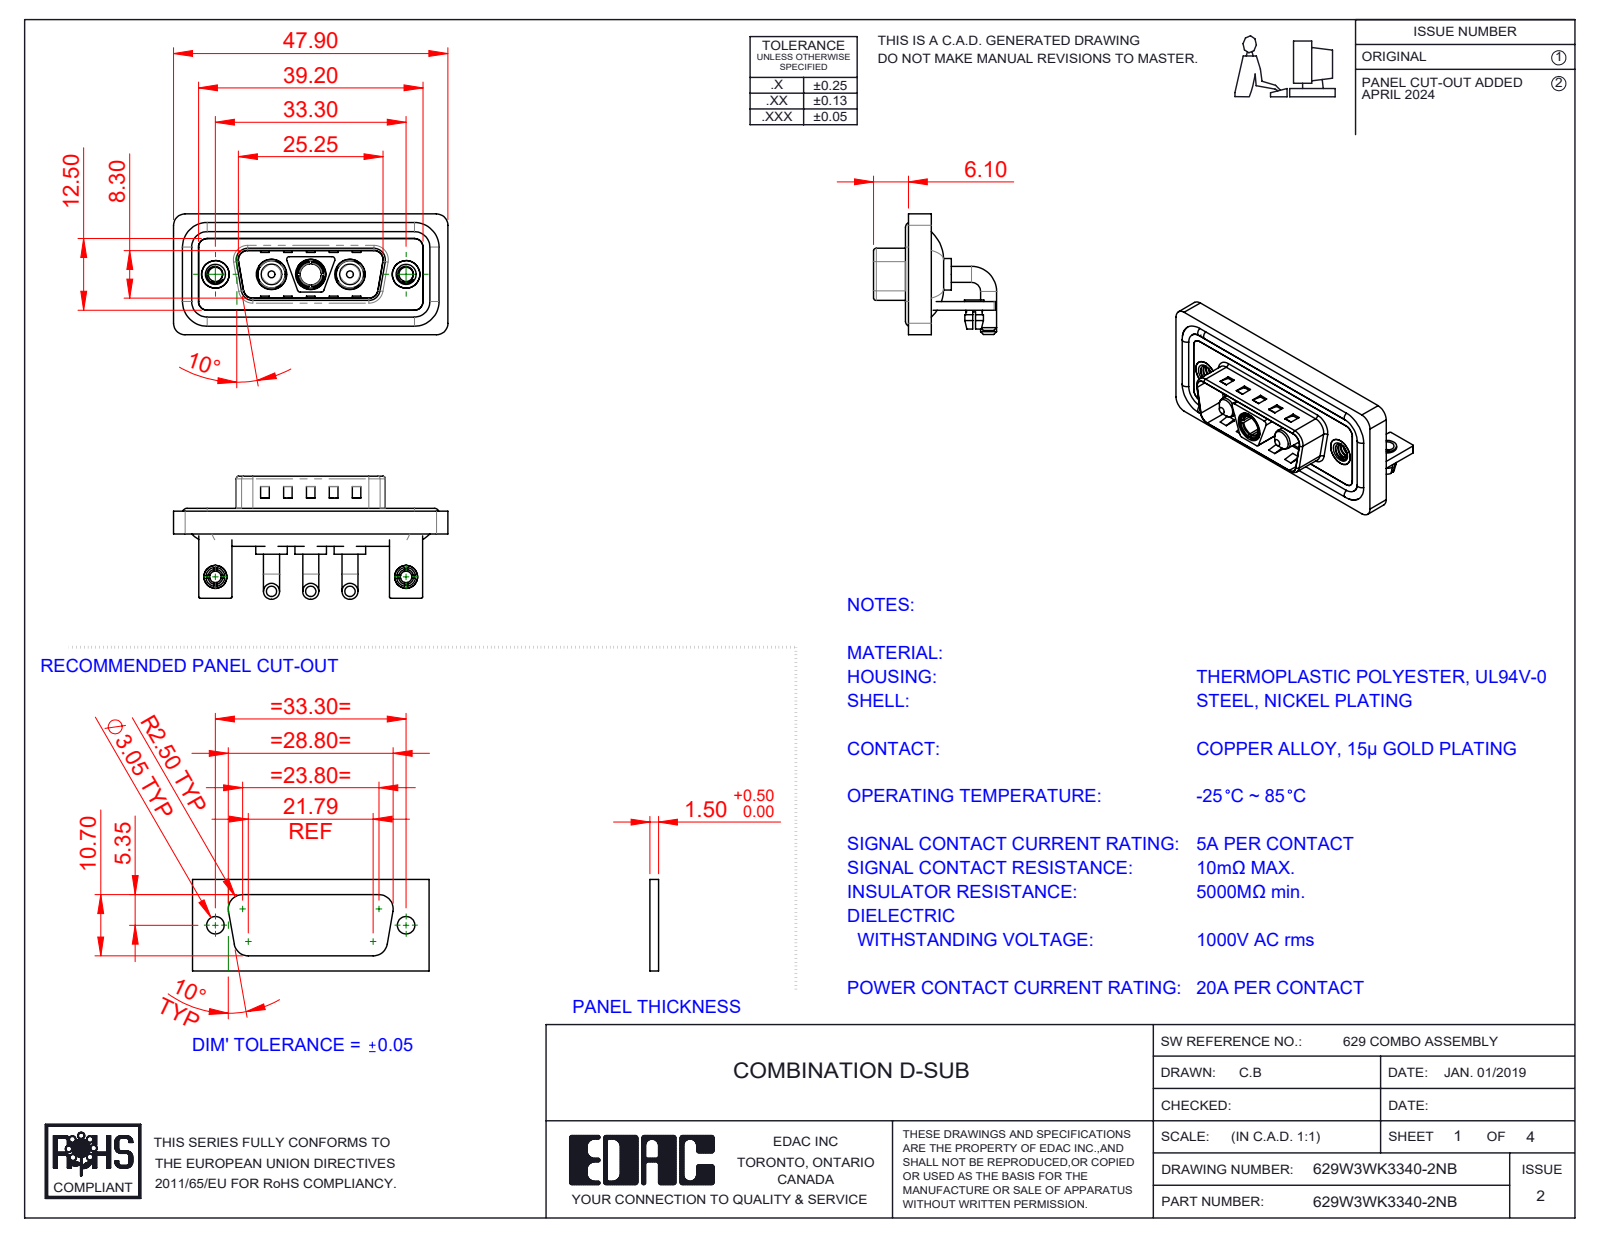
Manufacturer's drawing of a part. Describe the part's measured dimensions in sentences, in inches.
The part is named "629Combo Shell Rear_15 Contacts; 629Combo Stabilizer Bracket; 629Combo Waterproof Housing_15 Contacts; 629Combo Housing_3WK3 (+6 more)". Its 3-D file was written by "SolidWorks 2023 (CONFIG_CONTROL_DESIGN)". It is 17 solids with 751 faces: 299 planar, 306 cylindrical and 146 other. Overall it measures 1.886 by 0.846 by 0.831 inches. Its volume is 0.378 cubic inches and its surface area 15.83 square inches. Round holes: 4 of diameter 0.098, 3 of diameter 0.191, 3 of diameter 0.209, 2 of diameter 0.079, 2 of diameter 0.126, 2 of diameter 0.157, 2 of diameter 0.189, 2 of diameter 0.197, 1 of diameter 0.146. Round bosses or shafts: 6 of diameter 0.11, 4 of diameter 0.063, 3 of diameter 0.217, 3 of diameter 0.205, 3 of diameter 0.187, 3 of diameter 0.148, 2 of diameter 0.193, 2 of diameter 0.157. Partial cylindrical surfaces (rounded edges, fillets, slot ends): 21 of radius 0.079, 18 of radius 0.059, 16 of radius 0.01, 13 of radius 0.02, 8 of radius 0.063, 4 of radius 0.024, 4 of radius 0.026, 4 of radius 0.035. The main face-to-face distances are 0.016, 0.059, 0.031, 0.114, 0.043, 0.083, 0.146, 0.063, 0.047, 0.177. The hole center spacings are 0.27, 0.386, 0.656, 0.925, 1.311, 0.539.
